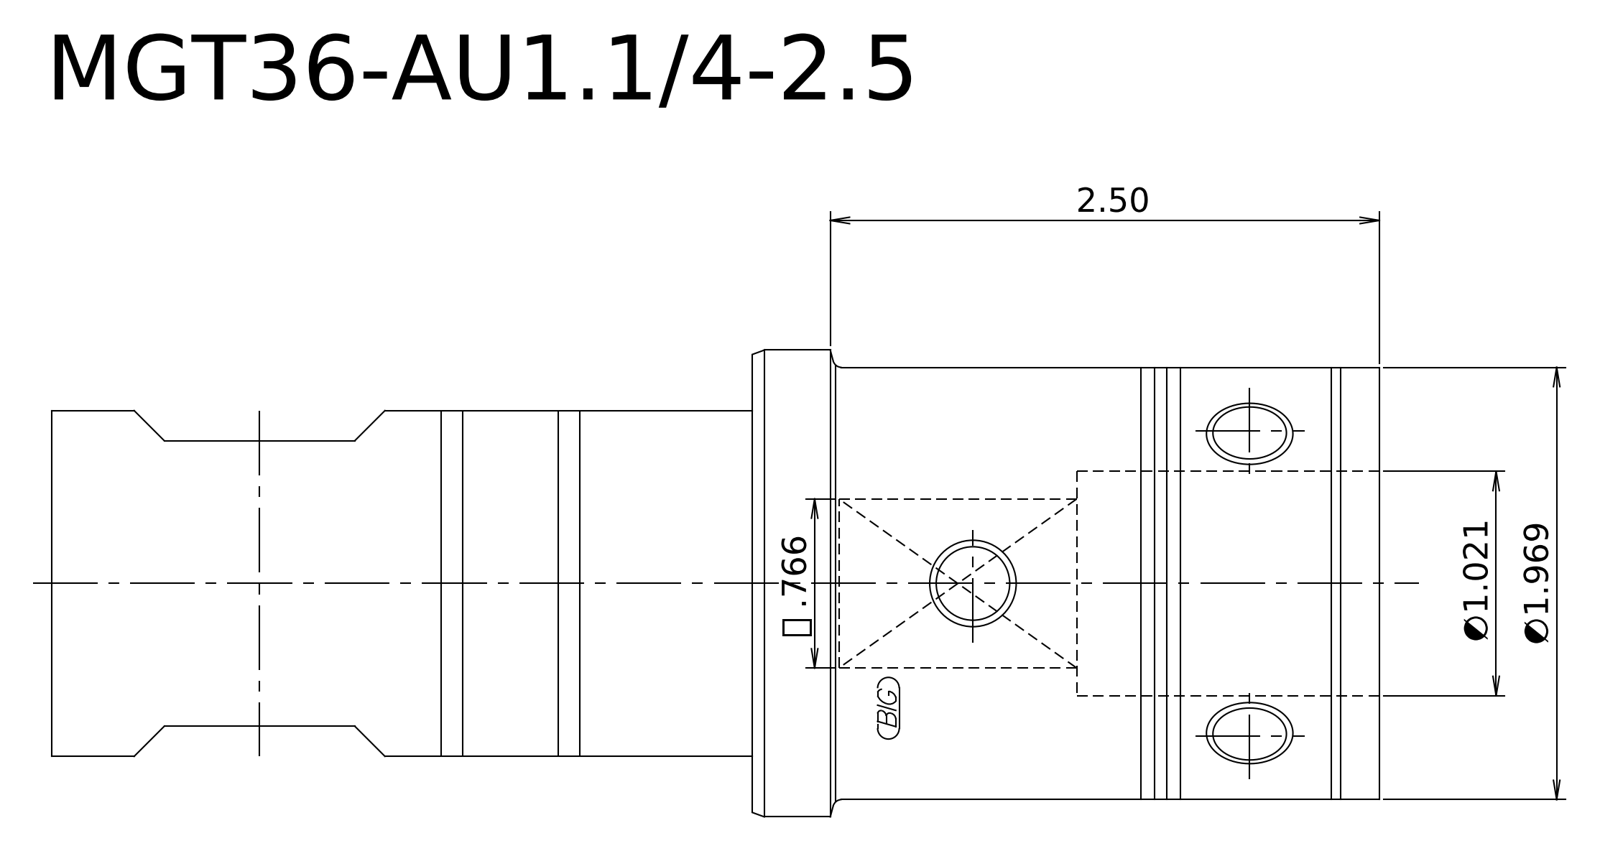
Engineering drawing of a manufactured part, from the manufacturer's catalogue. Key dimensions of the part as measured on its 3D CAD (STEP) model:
STEP written by: Kubotek KeyCreator 2011 V10.0.2 (22737) (automotive_design)
Units: millimetres
Bodies: 1 solid, 8 faces (3 planar, 3 cylindrical, 2 other)
Overall size (bounding box): 153.5 × 54 × 54
Volume: 247 234 mm³ · Surface area: 26 048 mm²
Round bosses / shafts (diameter × count): ⌀54 ×1, ⌀50 ×1, ⌀40 ×1
Main face-to-face distances: 153.5, 72.5, 81
